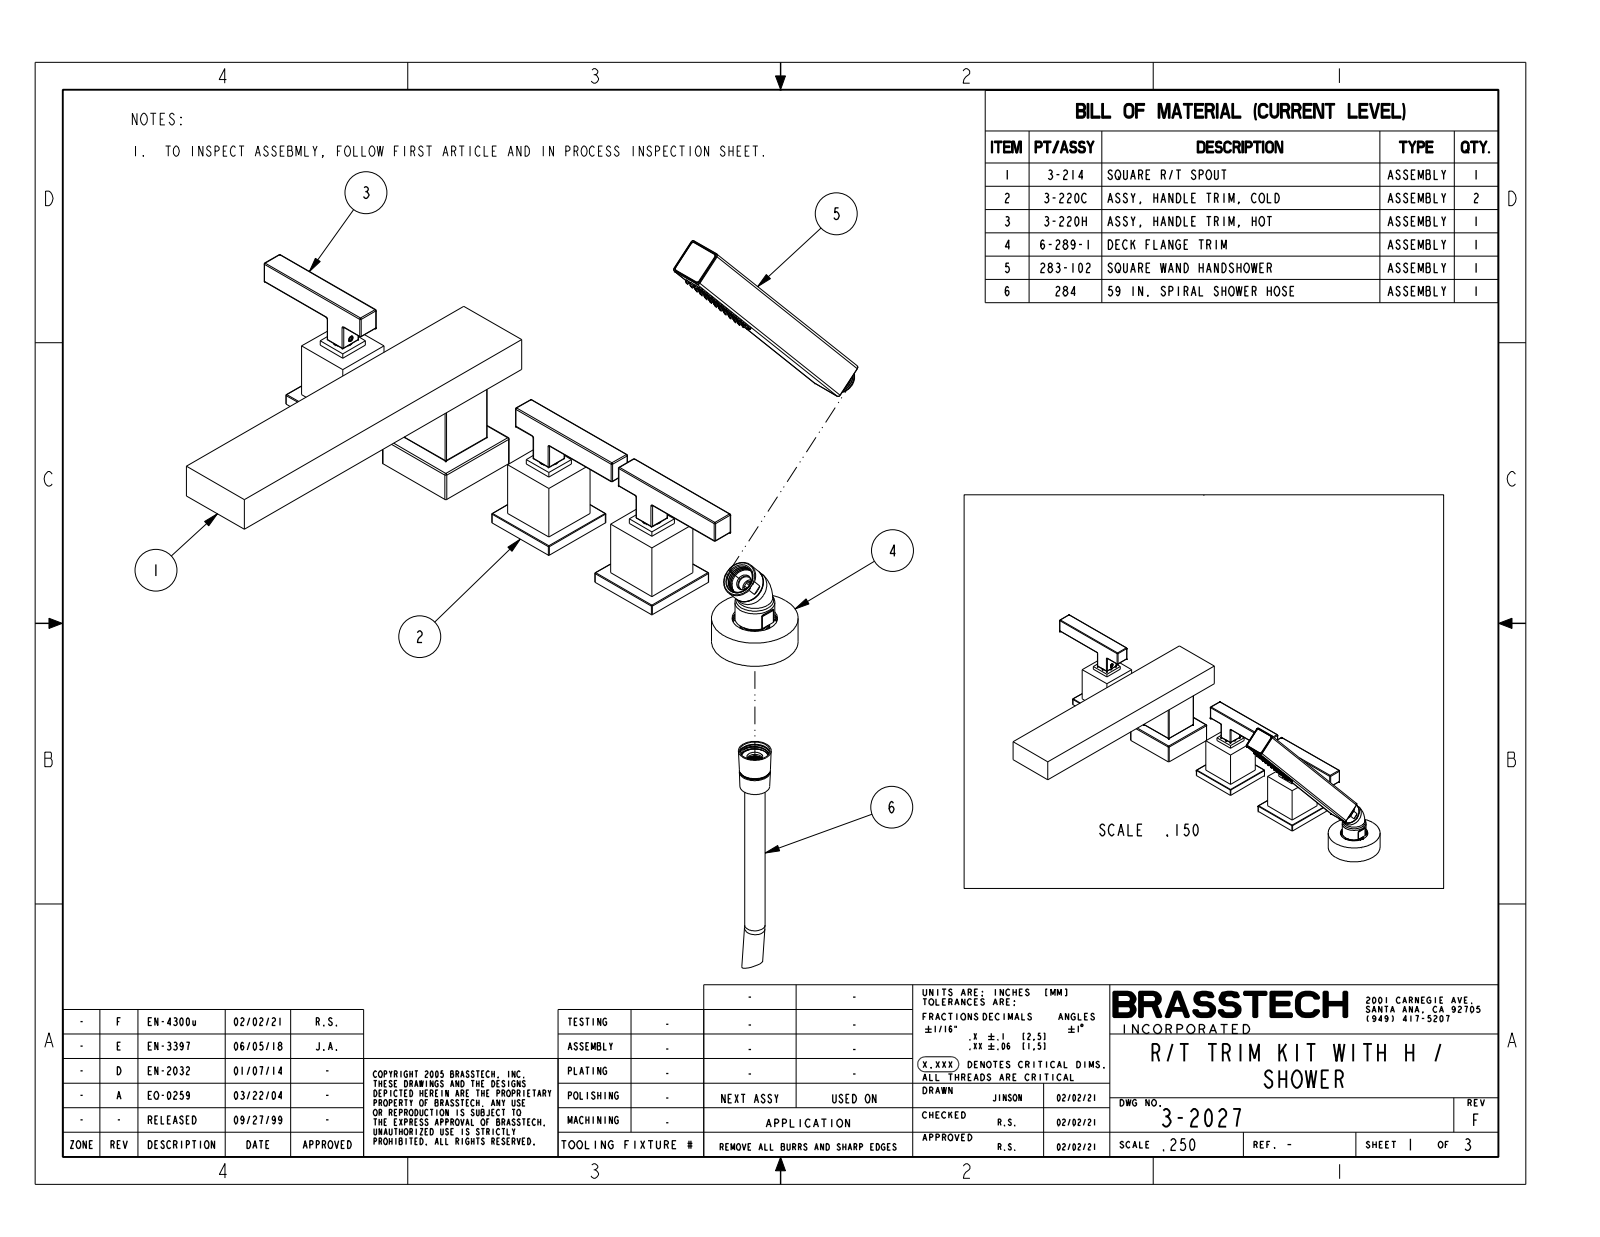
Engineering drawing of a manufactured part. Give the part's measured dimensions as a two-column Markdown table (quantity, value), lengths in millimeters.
| quantity | value |
| --- | --- |
| part name | 3-2027 |
| STEP written by | CREO PARAMETRIC BY PTC INC, 2018400 (CONFIG_CONTROL_DESIGN) |
| units | millimeters |
| bodies | 5 solids, 1161 faces (217 planar, 305 cylindrical, 639 other) |
| overall size | 506.7 × 273.6 × 236.7 |
| volume | 1 164 000 mm³ |
| surface area | 173 700 mm² |
| round holes (diameter × count) | 3.6 × 44, 3.9 × 1, 21.2 × 1 |
| round bosses / shafts (diameter × count) | 20.3 × 3, 10.2 × 3, 60.3 × 1, 27.8 × 1, 27.6 × 1, 26.4 × 1, 24.9 × 1, 24.8 × 1 |
| partial cylindrical surfaces (radius × count) | 0.8 × 66, 0.5 × 20, 0.3 × 16, 1 × 8, 1.3 × 6, 1.7 × 4, 12.7 × 2 |
| main face-to-face distances | 25.4, 96.8, 71.4, 40.6, 12.4, 28.3, 7.9, 57.2, 21.8, 49.5 |
| hole center spacings | 8.5, 4.3, 11.4, 17.1, 15.3, 29.8, 7.4, 22.1 |
